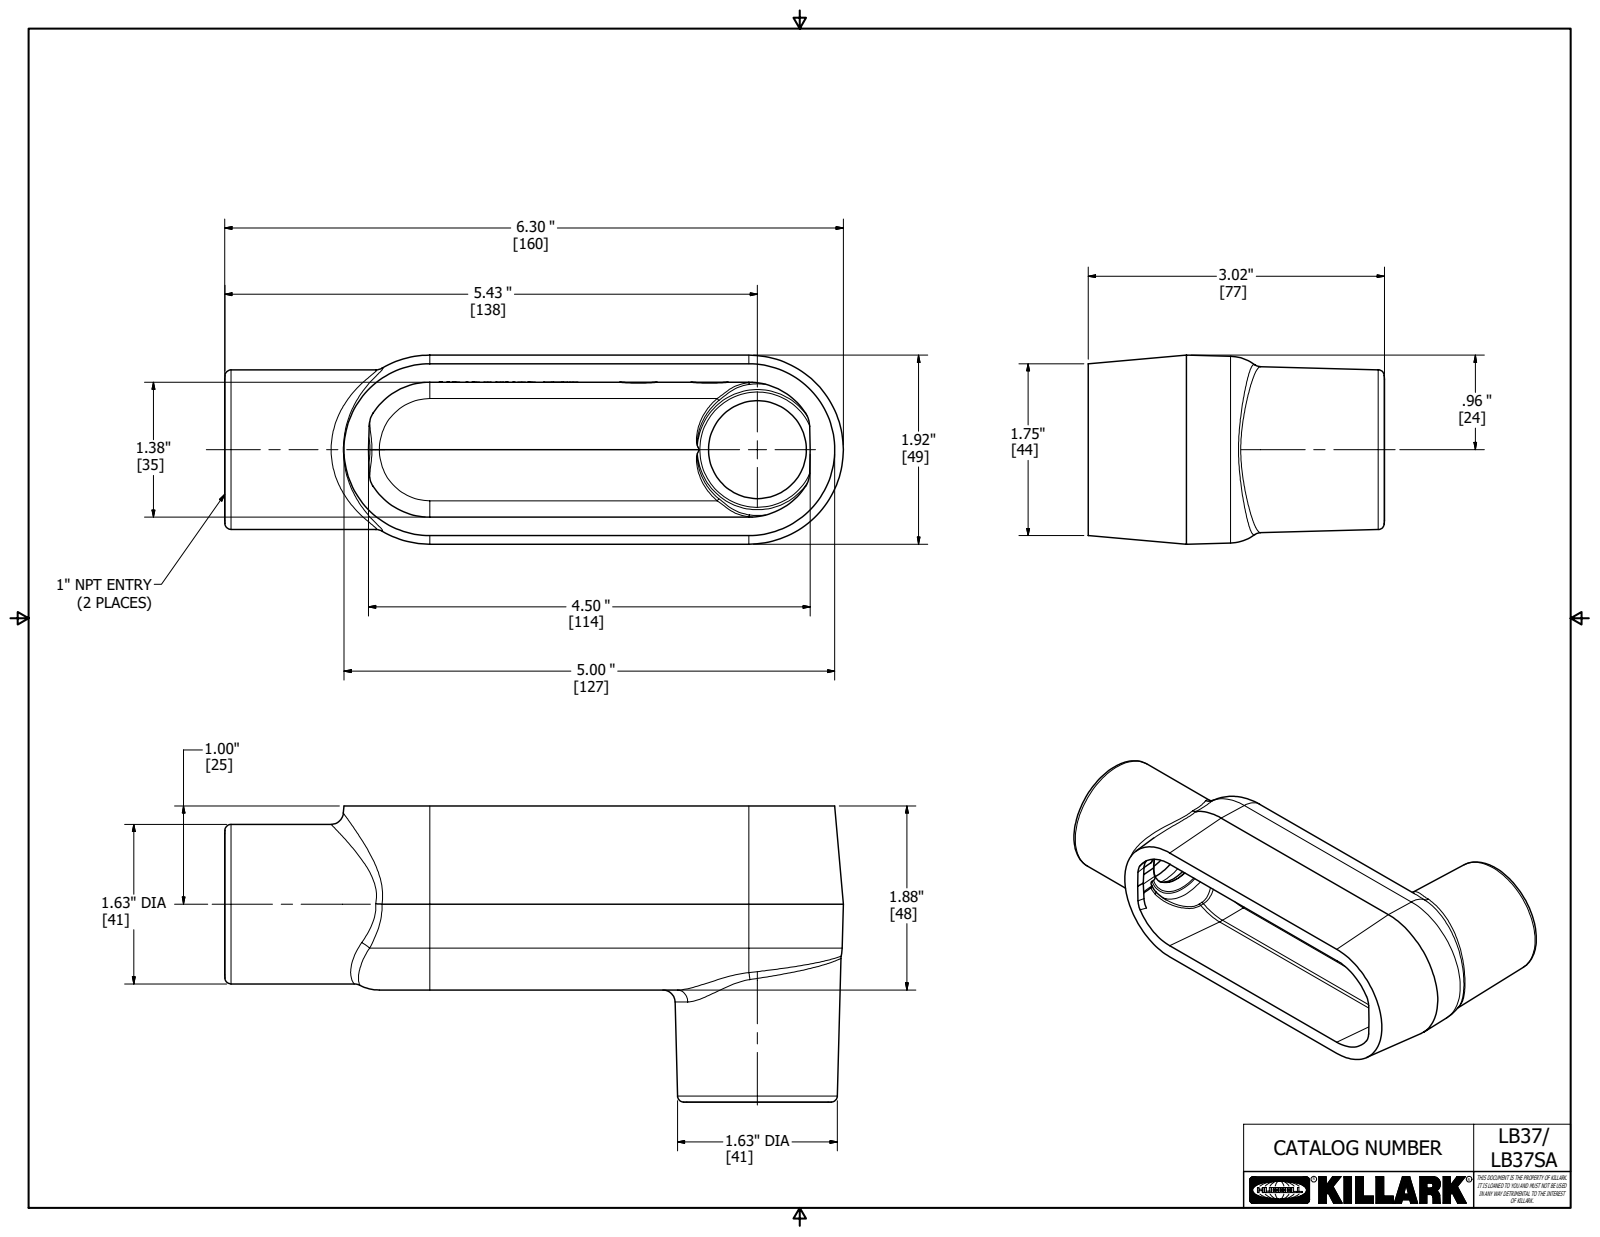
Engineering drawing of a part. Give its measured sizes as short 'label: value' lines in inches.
name: 17669-2
written by: Autodesk Inventor 2018 (AUTOMOTIVE_DESIGN)
unit: in
bodies: 1 solid, 872 faces (533 planar, 38 cylindrical, 301 other)
size: 6.302 × 3.017 × 1.925
volume: 7.117 in³; area: 77.19 in²
holes: 2× ⌀1.321, 1× ⌀0.047, 1× ⌀0.407, 1× ⌀1.344
bosses: 1× ⌀1.625, 1× ⌀0.5, 1× ⌀0.056
rounds: 6× R0.062, 4× R0.125, 3× R0.25, 2× R0.437, 2× R0.5, 1× R0.006, 1× R0.009, 1× R0.016
face distances: 0.187, 0.187, 1.875, 0.031, 1.844, 0.218, 1.578, 4.5, 0.039, 0.461
hole spacings: 0.122
